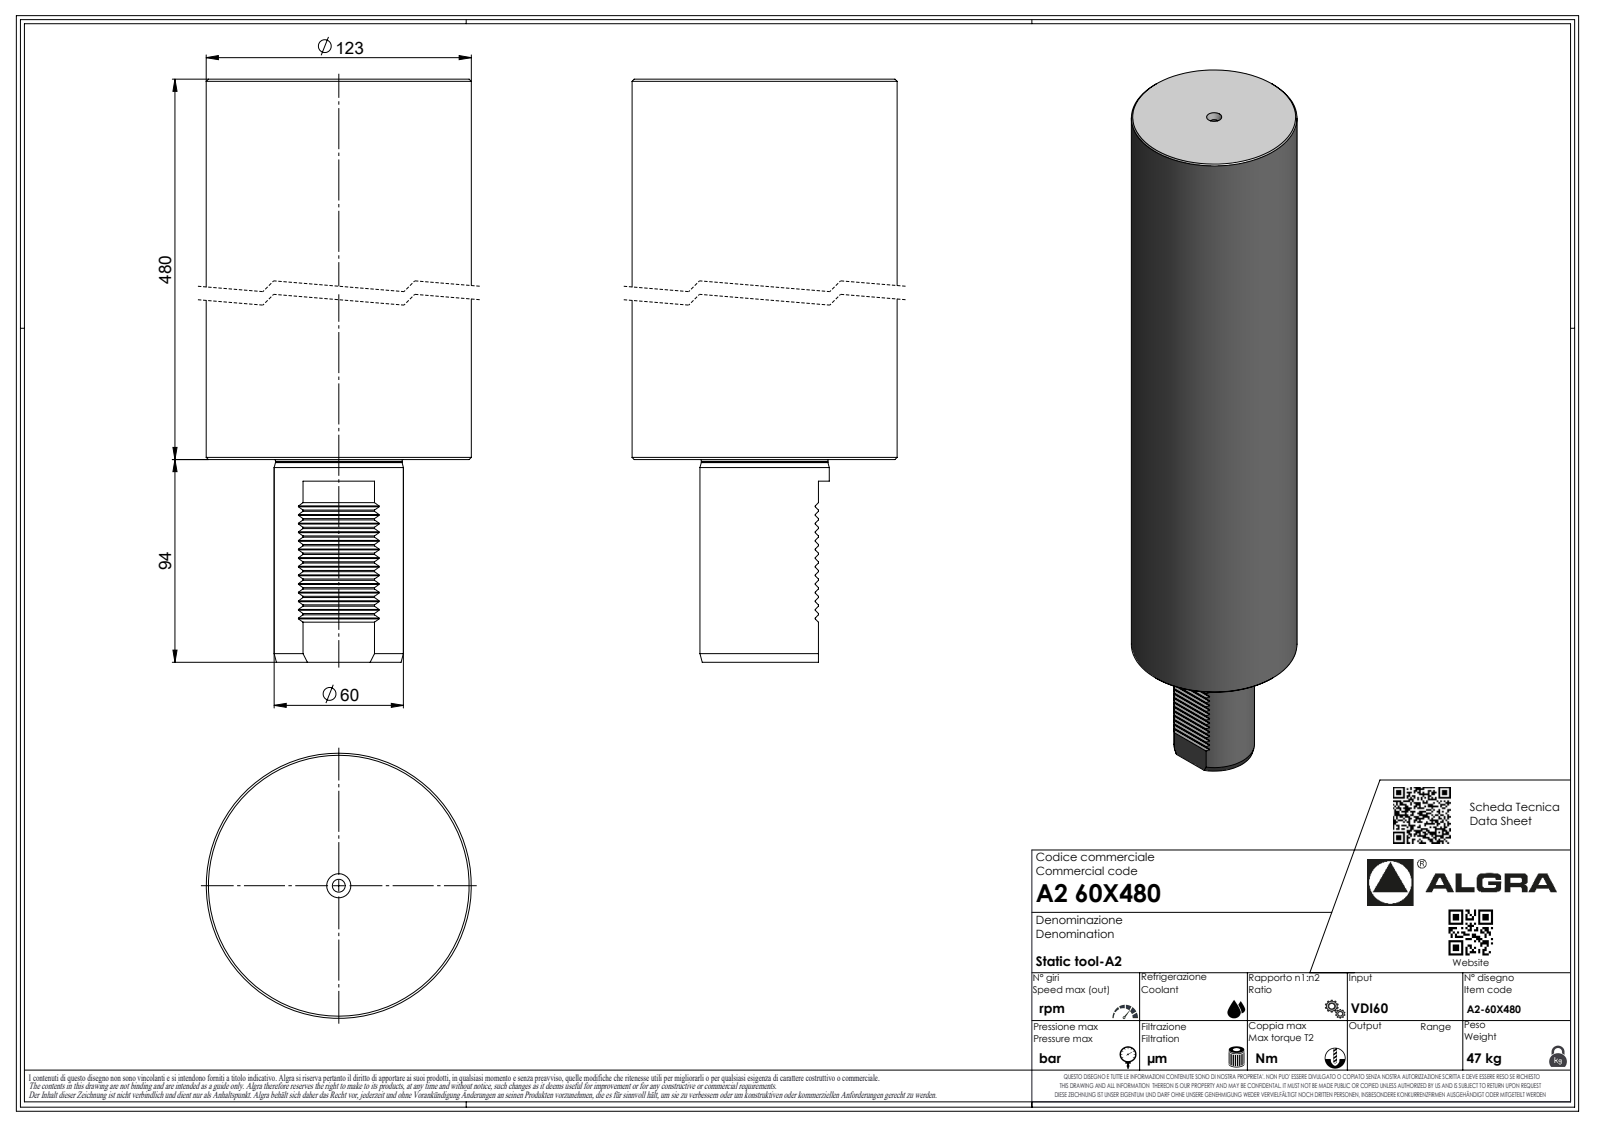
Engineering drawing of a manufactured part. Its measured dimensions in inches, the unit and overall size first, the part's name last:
Units: inches
Overall size (bounding box): 22.598 × 4.843 × 4.843
Round holes (diameter × count): ⌀0.083 ×1
Round bosses / shafts (diameter × count): ⌀4.843 ×1, ⌀2.362 ×1, ⌀2.311 ×1, ⌀0.251 ×1, ⌀0.067 ×1
Partial cylindrical surfaces — rounded edges, fillets, slot ends (radius × count): R0.012 ×14, R0.013 ×7, R0.02 ×7, R0.146 ×7, R0.008 ×1
Main face-to-face distances: 18.898, 3.701, 22.598, 0.111, 0.557, 0.445, 0.334, 0.223, 0.668, 0.222
Volume: 363.5 in³ · Surface area: 351.9 in²
Bodies: 1 solid, 300 faces (195 planar, 43 cylindrical, 62 other)
Part name (STEP PRODUCT): A260X480
STEP written by: SolidWorks 2023 (AUTOMOTIVE_DESIGN)
